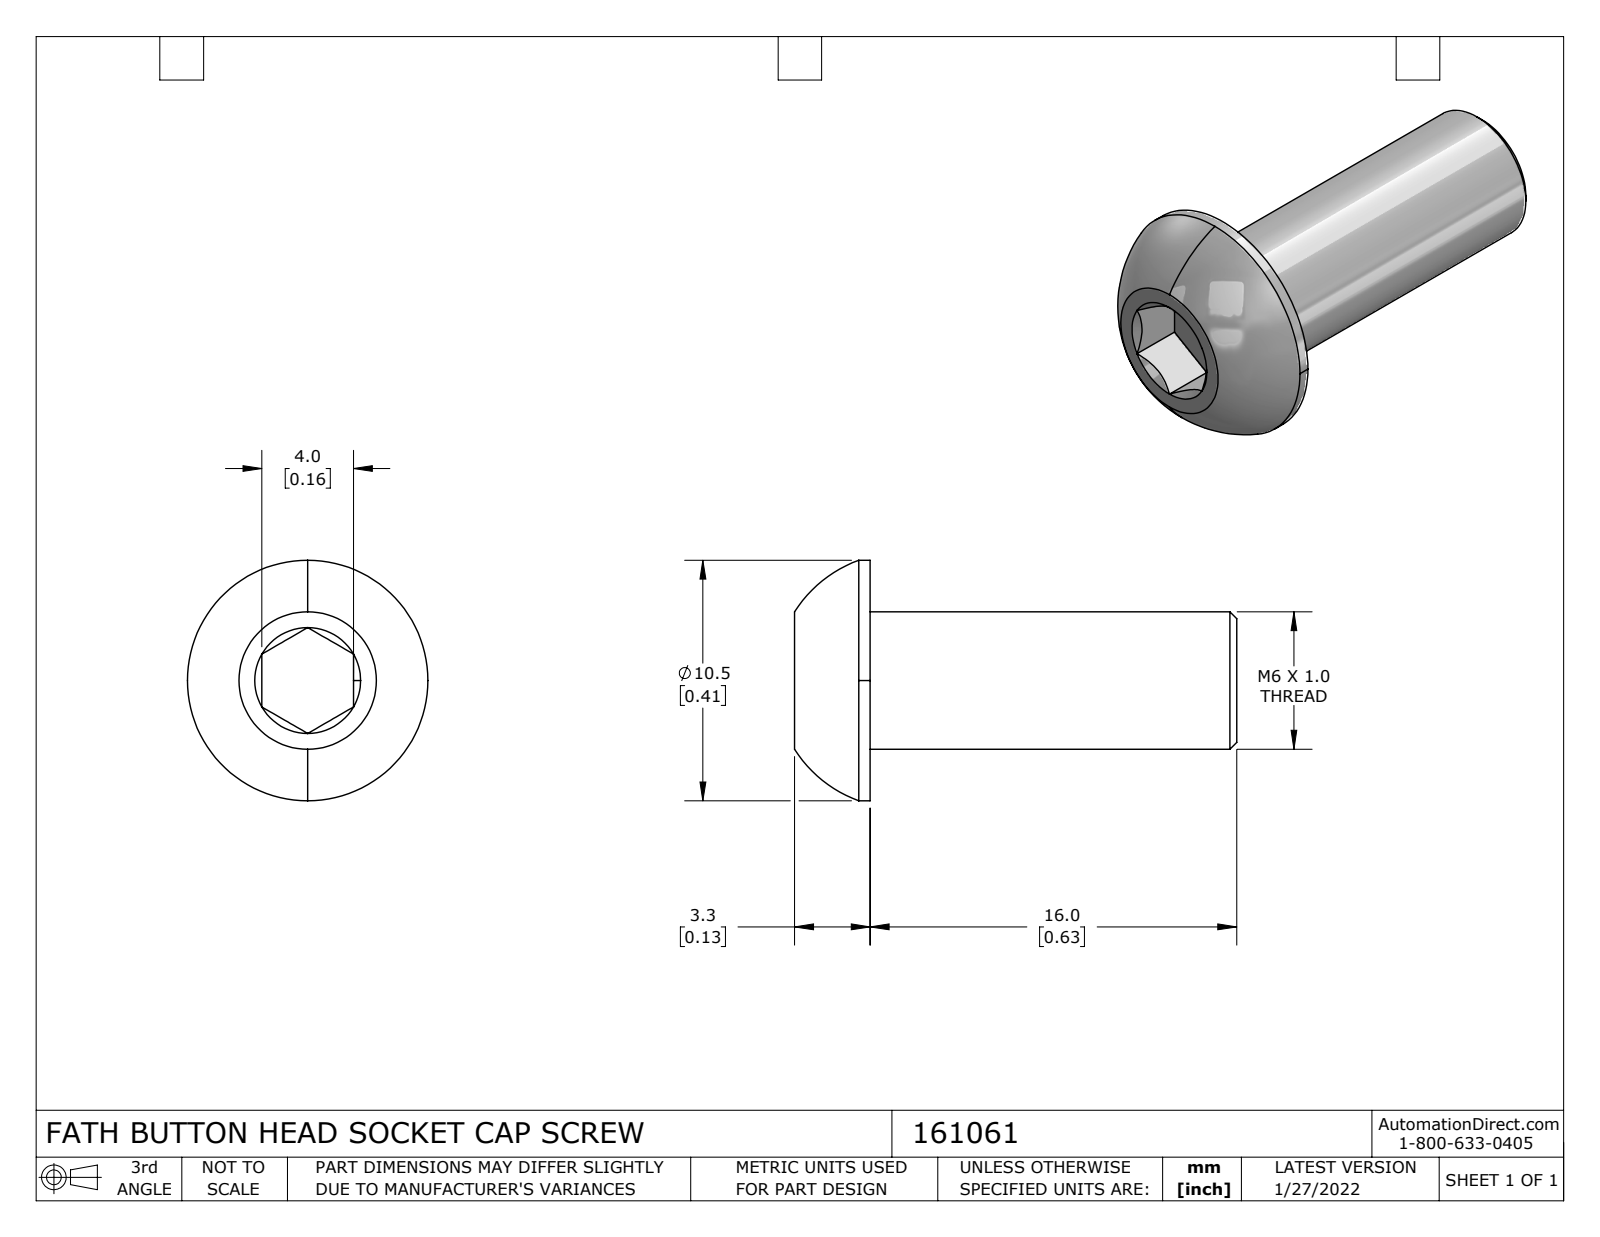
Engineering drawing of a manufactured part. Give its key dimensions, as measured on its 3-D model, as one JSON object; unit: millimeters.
{"part_name": "161061", "step_written_by": "SolidWorks 2021 (CONFIG_CONTROL_DESIGN)", "units": "millimeters", "bodies": {"solids": 1, "faces": 25, "planar": 10, "cylindrical": 4, "other": 11}, "overall_size": [19.3, 10.5, 10.5], "volume_mm3": 635, "surface_area_mm2": 558, "round_bosses_or_shafts": [[10.5, 1], [6, 1]], "face_to_face_distances": [16, 4, 16.99, 0.99, 19.3, 3.3, 2.31]}
